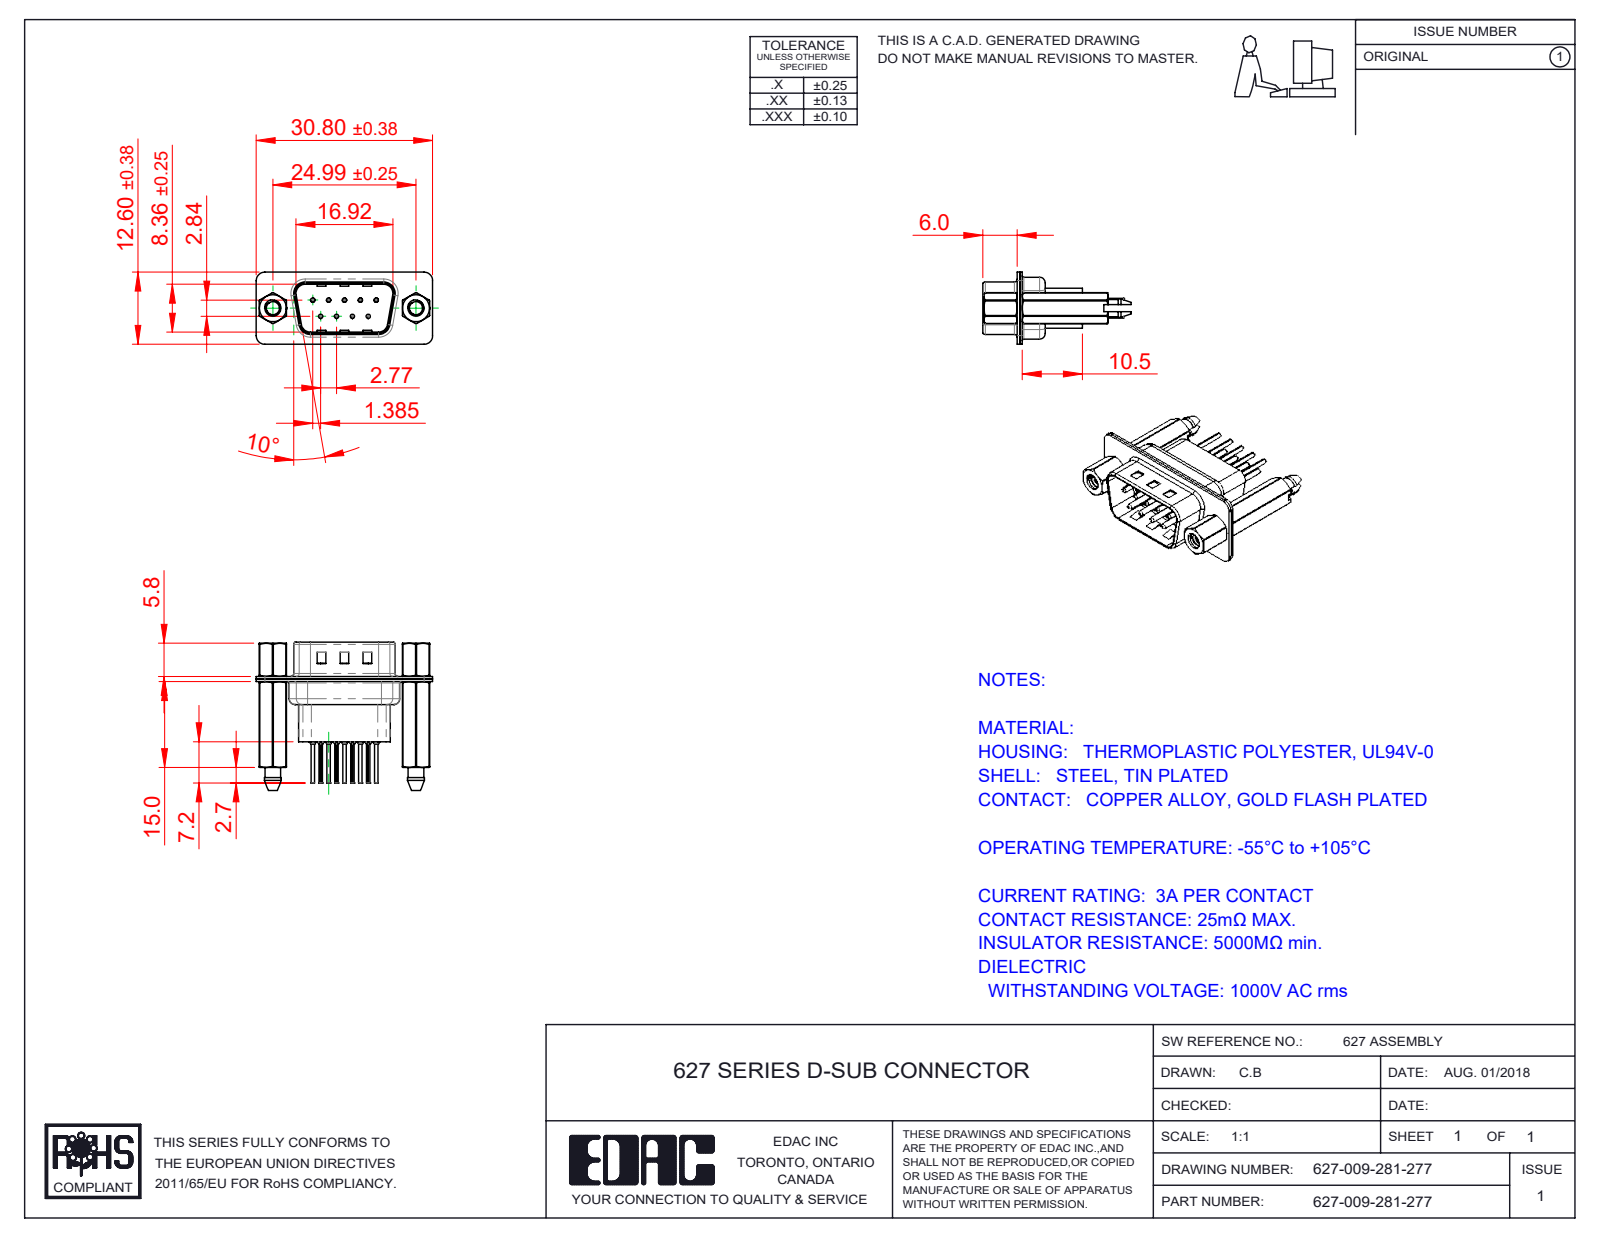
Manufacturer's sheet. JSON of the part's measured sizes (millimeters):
{"part_name": "627 Housing_09 HP; 627 Contact Row 2_61; 627 Shell Rear_09 Contacts; 627 Shell Front_09 Contacts (+4 more)", "step_written_by": "SolidWorks 2020 (CONFIG_CONTROL_DESIGN)", "units": "millimeters", "bodies": {"solids": 16, "faces": 1420, "planar": 377, "cylindrical": 600, "other": 443}, "overall_size": [30.8, 25.9, 12.6], "volume_mm3": 2375, "surface_area_mm2": 6060, "round_holes": [[0.2, 9], [0.35, 9], [1.1, 9], [1.6, 9], [2.26, 2], [2.29, 2], [4, 2], [4.8, 2]], "round_bosses_or_shafts": [[2, 9], [1.5, 9], [0.75, 9], [0.6, 9], [4.9, 2], [2.79, 2]], "partial_cylinders_radius": [[1.5, 20], [0.1, 18], [2, 12], [1.6, 10], [0.5, 8], [0.25, 4], [0.6, 4], [0.65, 4]], "face_to_face_distances": [0.45, 0.4, 0.9, 4.76, 0.82, 9.58, 1.4, 1.5, 0.68, 7.68], "hole_center_spacings": [3.16, 2.77, 5.54, 5.03, 5.04, 8.31, 7.48, 7.49]}
